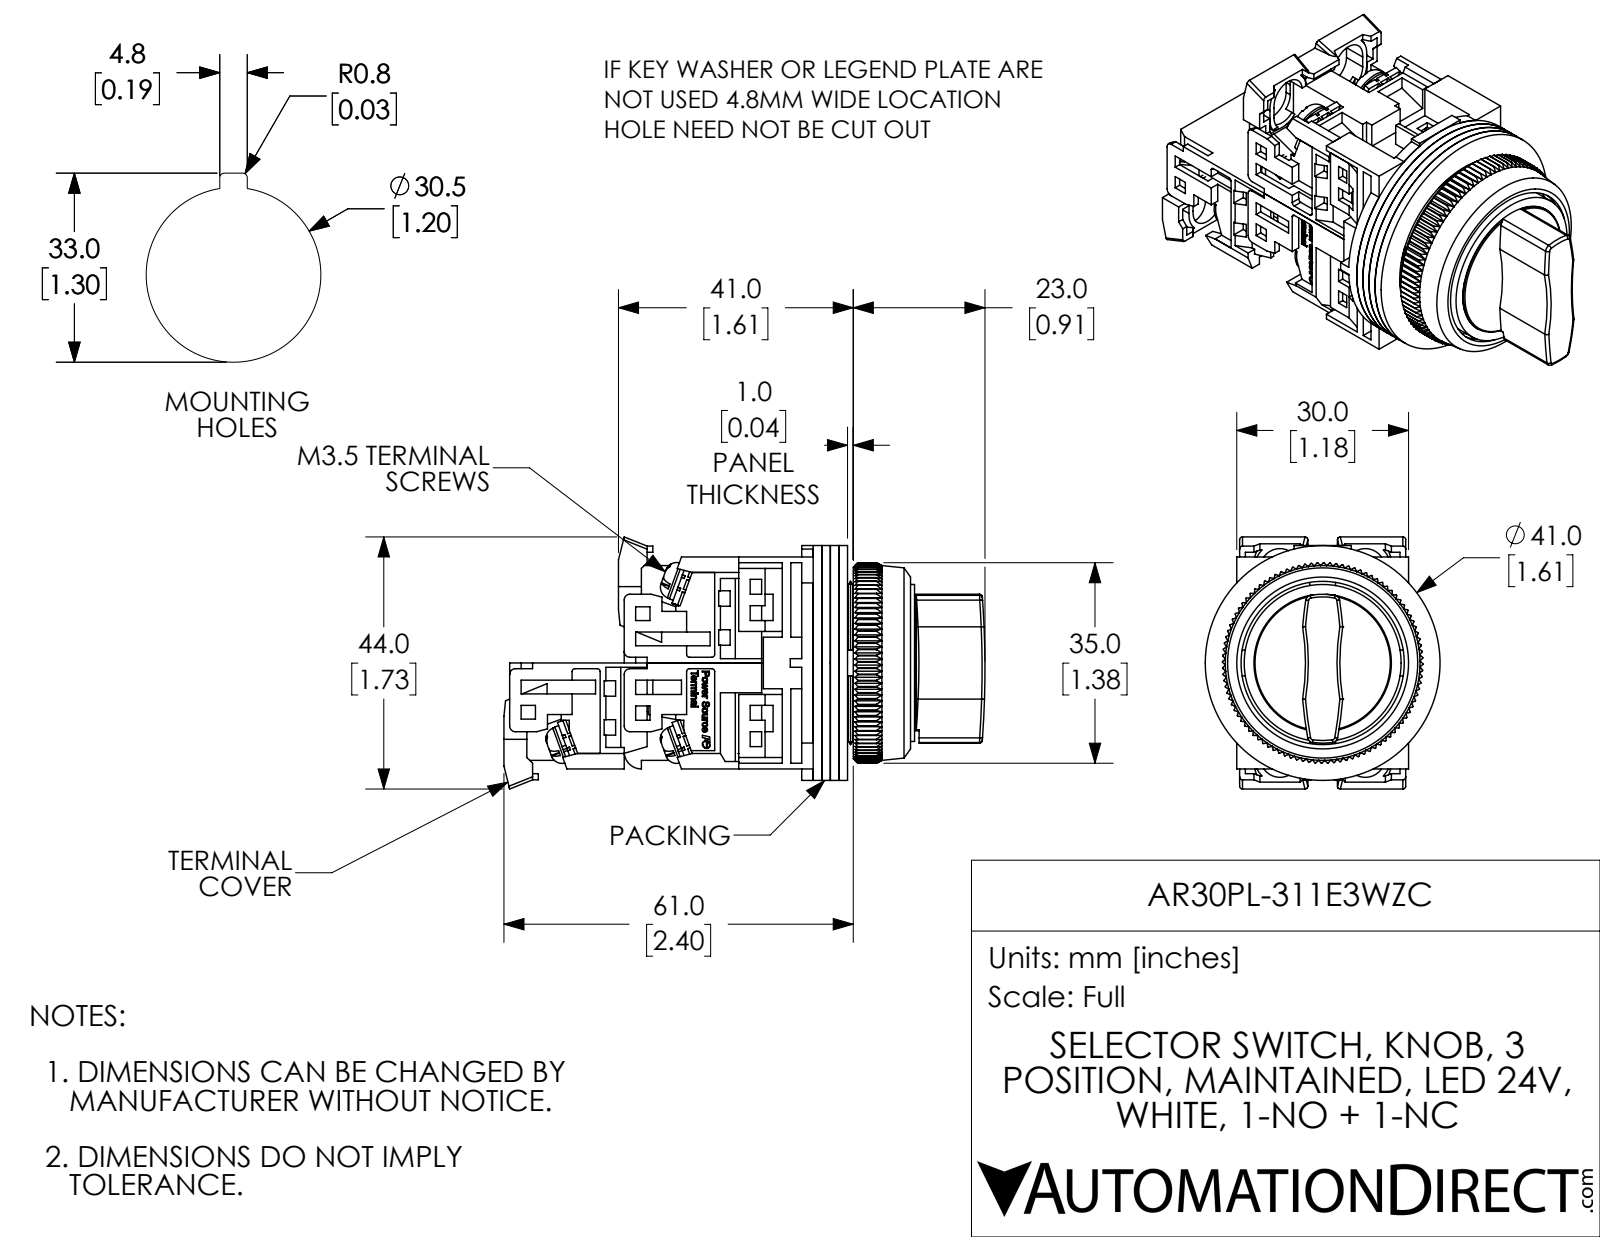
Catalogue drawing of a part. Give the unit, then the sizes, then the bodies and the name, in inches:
Units: inches
Overall size (bounding box): 3.307 × 1.732 × 1.614
Round holes (diameter × count): ⌀0.138 ×10, ⌀0.142 ×6, ⌀0.118 ×1, ⌀0.472 ×1, ⌀0.709 ×1, ⌀0.768 ×1, ⌀0.827 ×1, ⌀1.122 ×1, ⌀1.181 ×1, ⌀1.252 ×1
Round bosses / shafts (diameter × count): ⌀0.26 ×6, ⌀0.138 ×6, ⌀0.063 ×2, ⌀1.614 ×1, ⌀1.15 ×1, ⌀1.079 ×1, ⌀0.945 ×1, ⌀0.886 ×1
Partial cylindrical surfaces — rounded edges, fillets, slot ends (radius × count): R0.059 ×24, R0.02 ×14, R0.039 ×10, R0.138 ×4, R0.177 ×4, R0.118 ×3, R1.575 ×2, R2.953 ×2
Main face-to-face distances: 0.059, 0.118, 0.177, 0.039, 0.787, 0.063, 0.079, 0.02, 0.811, 0.689
Hole centre spacings: 0.579, 0.269, 0.638, 0.61
Volume: 2.677 in³ · Surface area: 66.54 in²
Bodies: 32 solids, 2783 faces (2039 planar, 338 cylindrical, 406 other)
Part name (STEP PRODUCT): AR30PL-311E3WZC
STEP written by: SolidWorks 2017 (AUTOMOTIVE_DESIGN)
